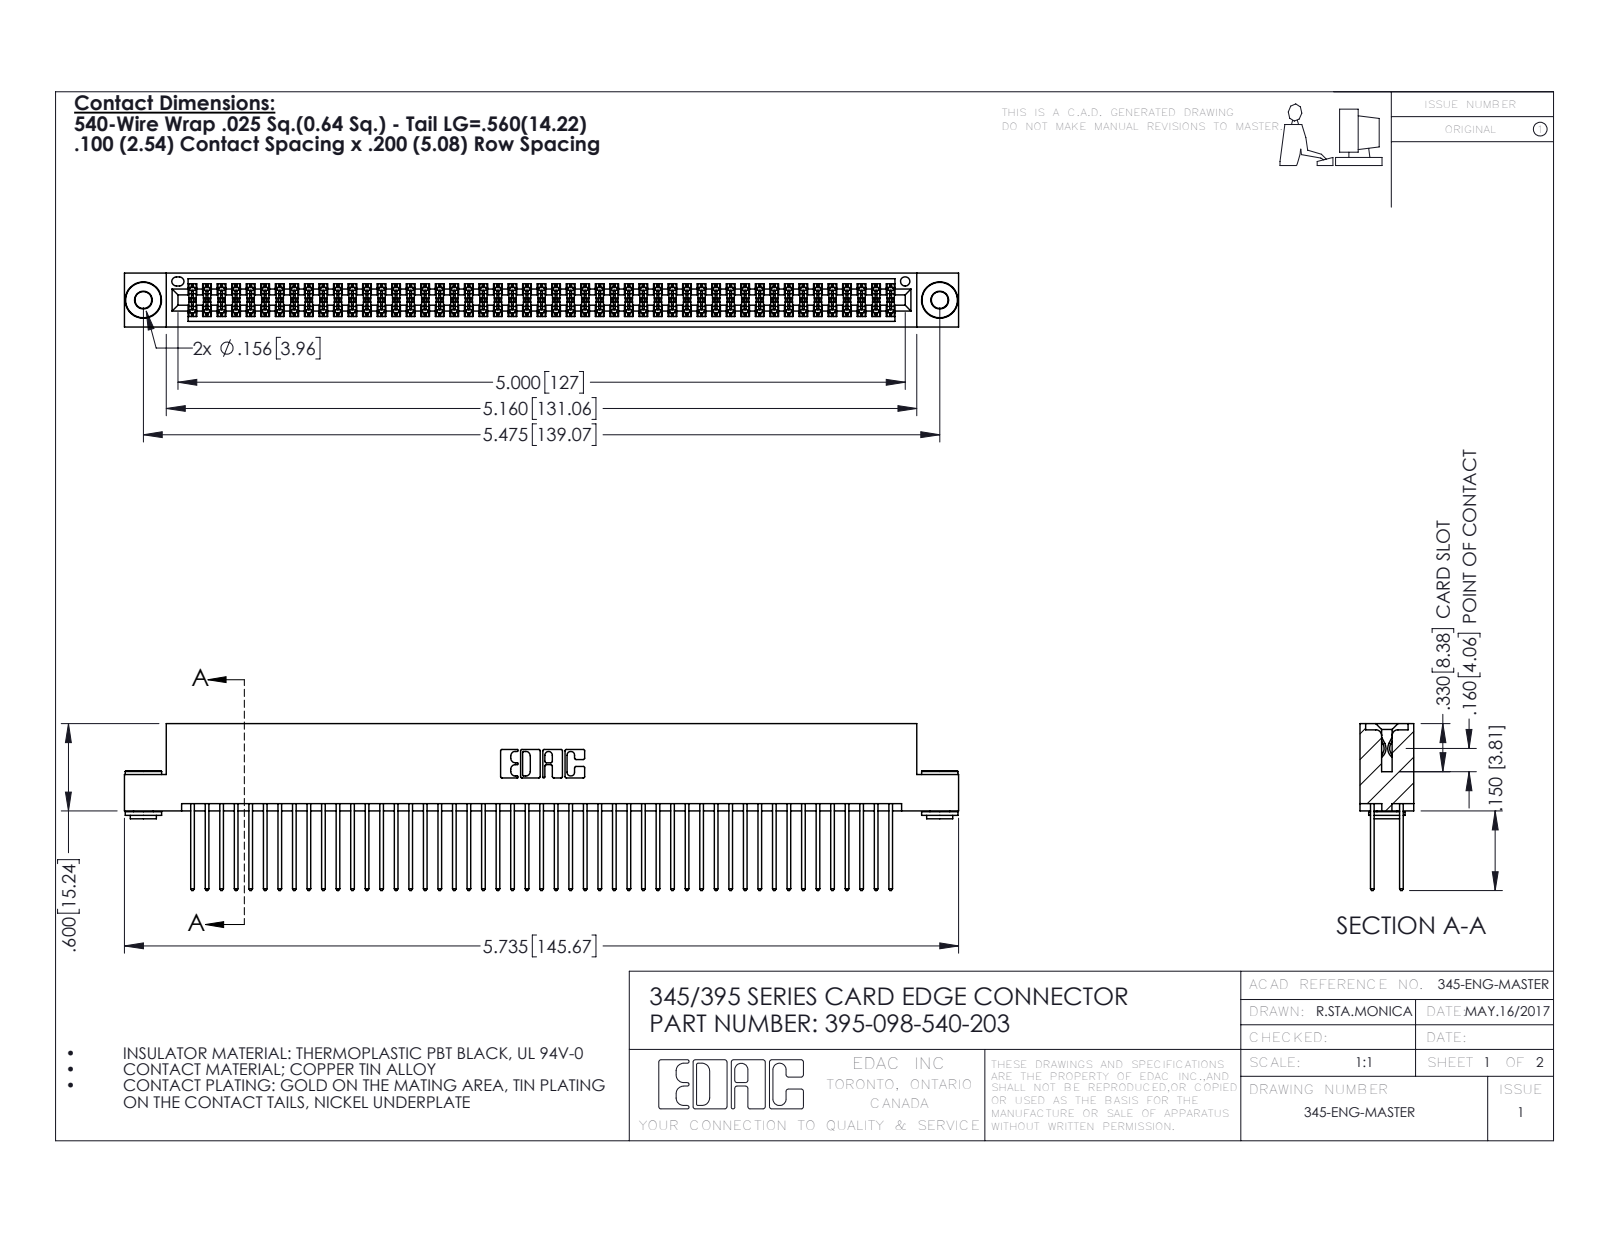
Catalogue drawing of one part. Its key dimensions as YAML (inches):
part_name: "345 Part_Flush Mounting Lugs - 0.156 Dia-TH; 345-250-002_345-250-002-102; 395-098-540-203; 345-292-001_345-293-140"
step_written_by: "SolidWorks 2016 (CONFIG_CONTROL_DESIGN)"
units: inches
bodies: {solids: 101, faces: 5064, planar: 3324, cylindrical: 1732, other: 8}
overall_size: [5.735, 1.147, 0.37]
volume: 0.891
surface_area: 36.66
round_holes:
  - {diameter: 0.116, count: 2}
  - {diameter: 0.156, count: 2}
  - {diameter: 0.064, count: 1}
round_bosses_or_shafts:
  - {diameter: 0.25, count: 2}
  - {diameter: 0.18, count: 2}
  - {diameter: 0.136, count: 2}
partial_cylinders:
  - {radius: 0.006, count: 147}
  - {radius: 0.01, count: 98}
  - {radius: 0.01, count: 22}
  - {radius: 0.007, count: 6}
  - {radius: 0.031, count: 6}
  - {radius: 0.026, count: 3}
  - {radius: 0.014, count: 2}
  - {radius: 0.019, count: 2}
face_to_face_distances: [0.072, 0.298, 0.2, 0.025, 0.098, 0.272, 0.225, 0.37, 0.175, 0.149]
hole_center_spacings: [0.27, 5.239, 5.475]
